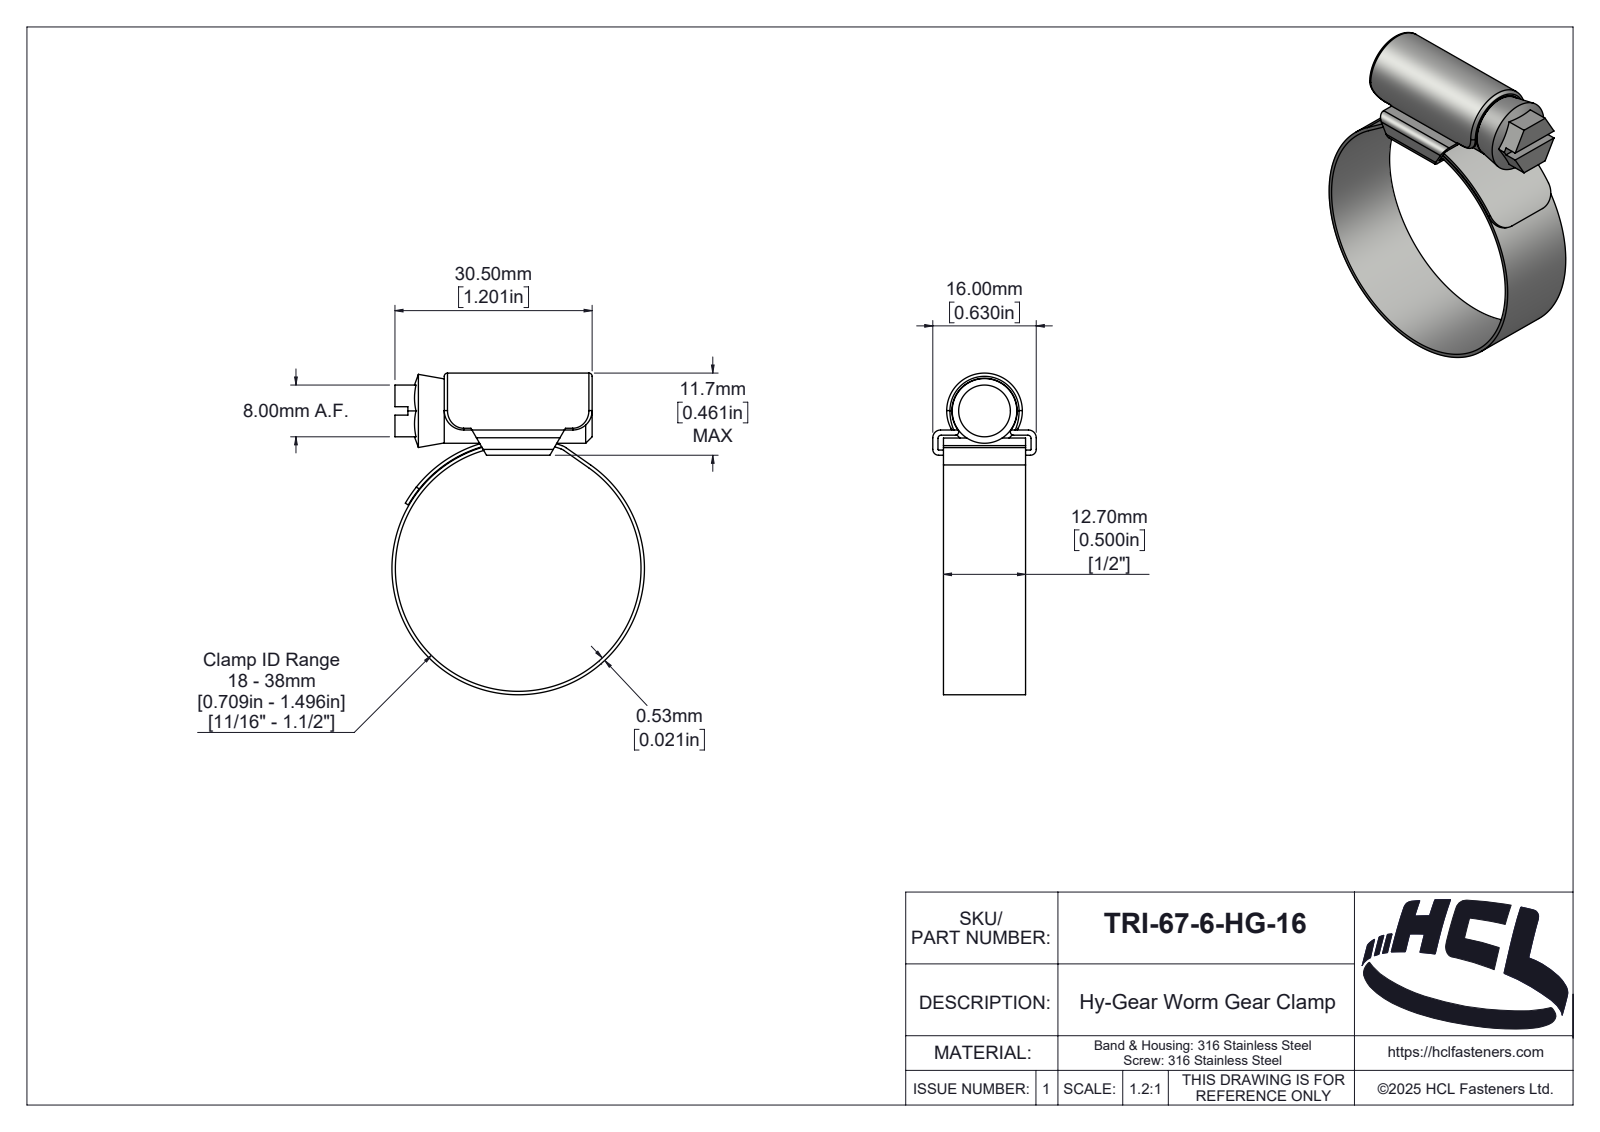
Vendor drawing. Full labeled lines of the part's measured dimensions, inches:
Part name (STEP PRODUCT): TRI-57-0-HG-16
STEP written by: SolidWorks 2025 (AUTOMOTIVE_DESIGN)
Units: inches
Bodies: 3 solids, 189 faces (39 planar, 89 cylindrical, 61 other)
Overall size (bounding box): 1.958 × 1.538 × 0.63
Volume: 0.241 in³ · Surface area: 10.33 in²
Round holes (diameter × count): ⌀1.496 ×1
Round bosses / shafts (diameter × count): ⌀1.538 ×1, ⌀0.394 ×1
Partial cylindrical surfaces — rounded edges, fillets, slot ends (radius × count): R0.02 ×6, R0.118 ×4, R0.004 ×2, R0.035 ×2, R0.047 ×2, R0.018 ×1, R0.074 ×1, R0.079 ×1
Main face-to-face distances: 0.031, 0.122, 0.091, 0.5, 0.021, 0.154, 1.201, 0.065, 0.565, 0.598
